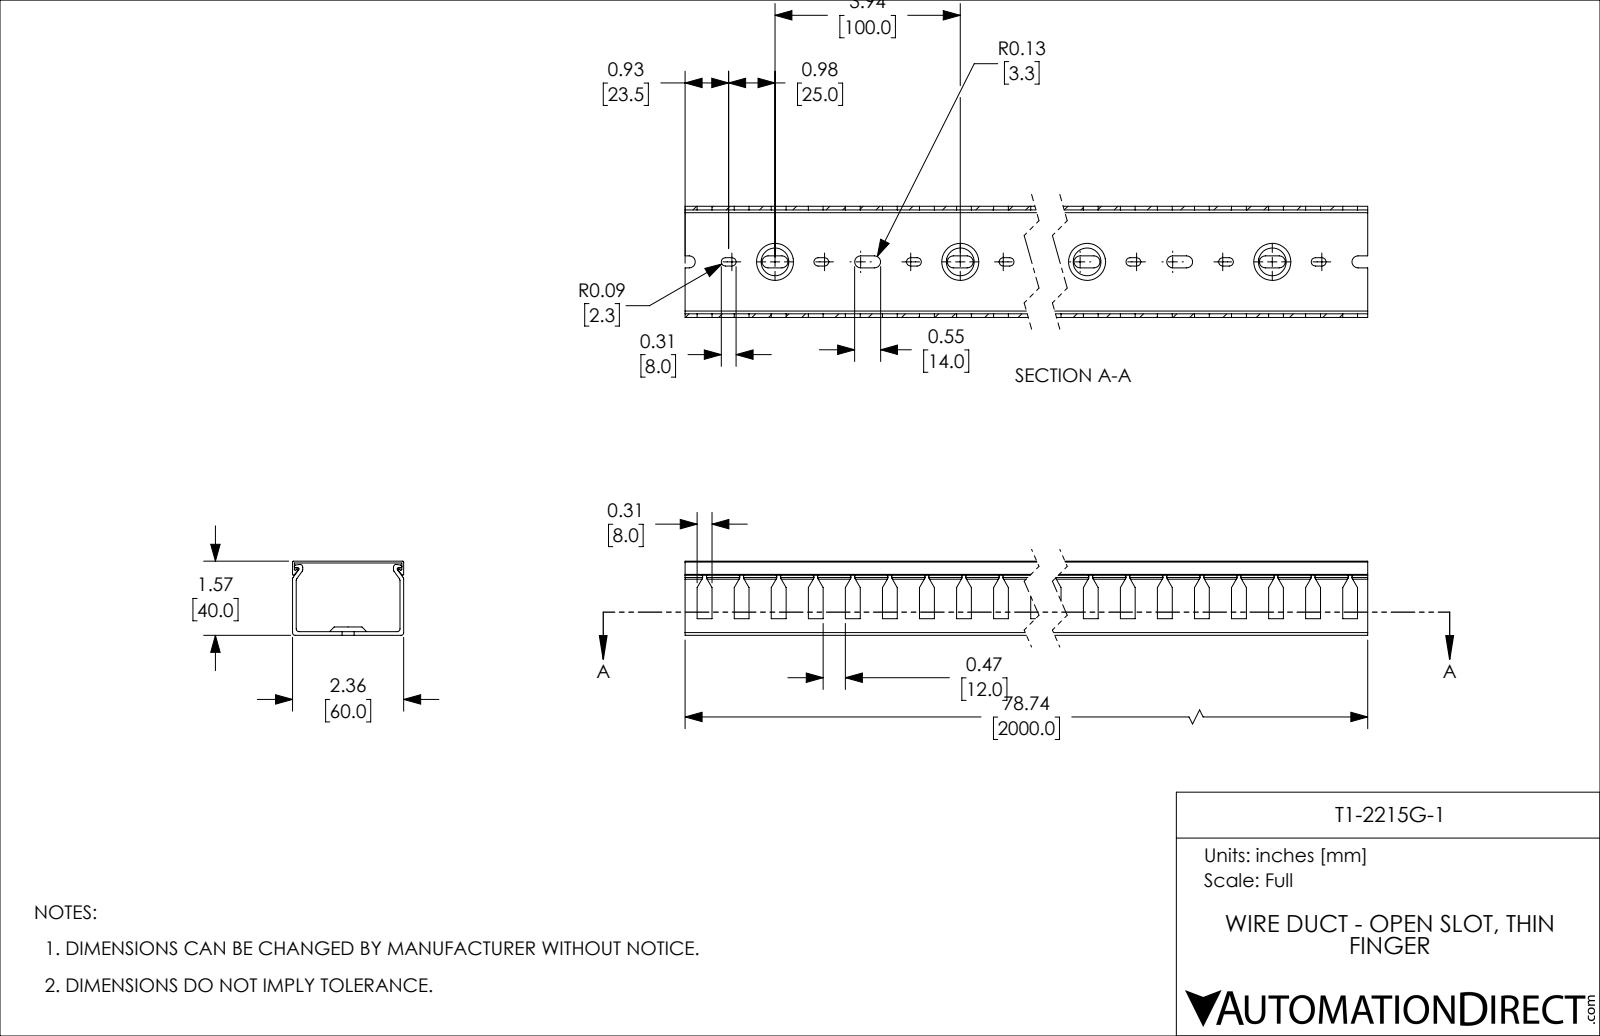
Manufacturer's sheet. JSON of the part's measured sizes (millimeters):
{"part_name": "T1-2215B-1", "step_written_by": "SolidWorks 2021 (CONFIG_CONTROL_DESIGN)", "units": "millimeters", "bodies": {"solids": 2, "faces": 1005, "planar": 534, "cylindrical": 431, "other": 40}, "overall_size": [2000, 60, 40], "volume_mm3": 701112, "surface_area_mm2": 856302, "partial_cylinders_radius": [[2.25, 80], [3.25, 80], [1.5, 12], [0.5, 8], [0.75, 6]], "face_to_face_distances": [2, 1, 40, 39, 58, 37, 38, 60, 56, 59]}
